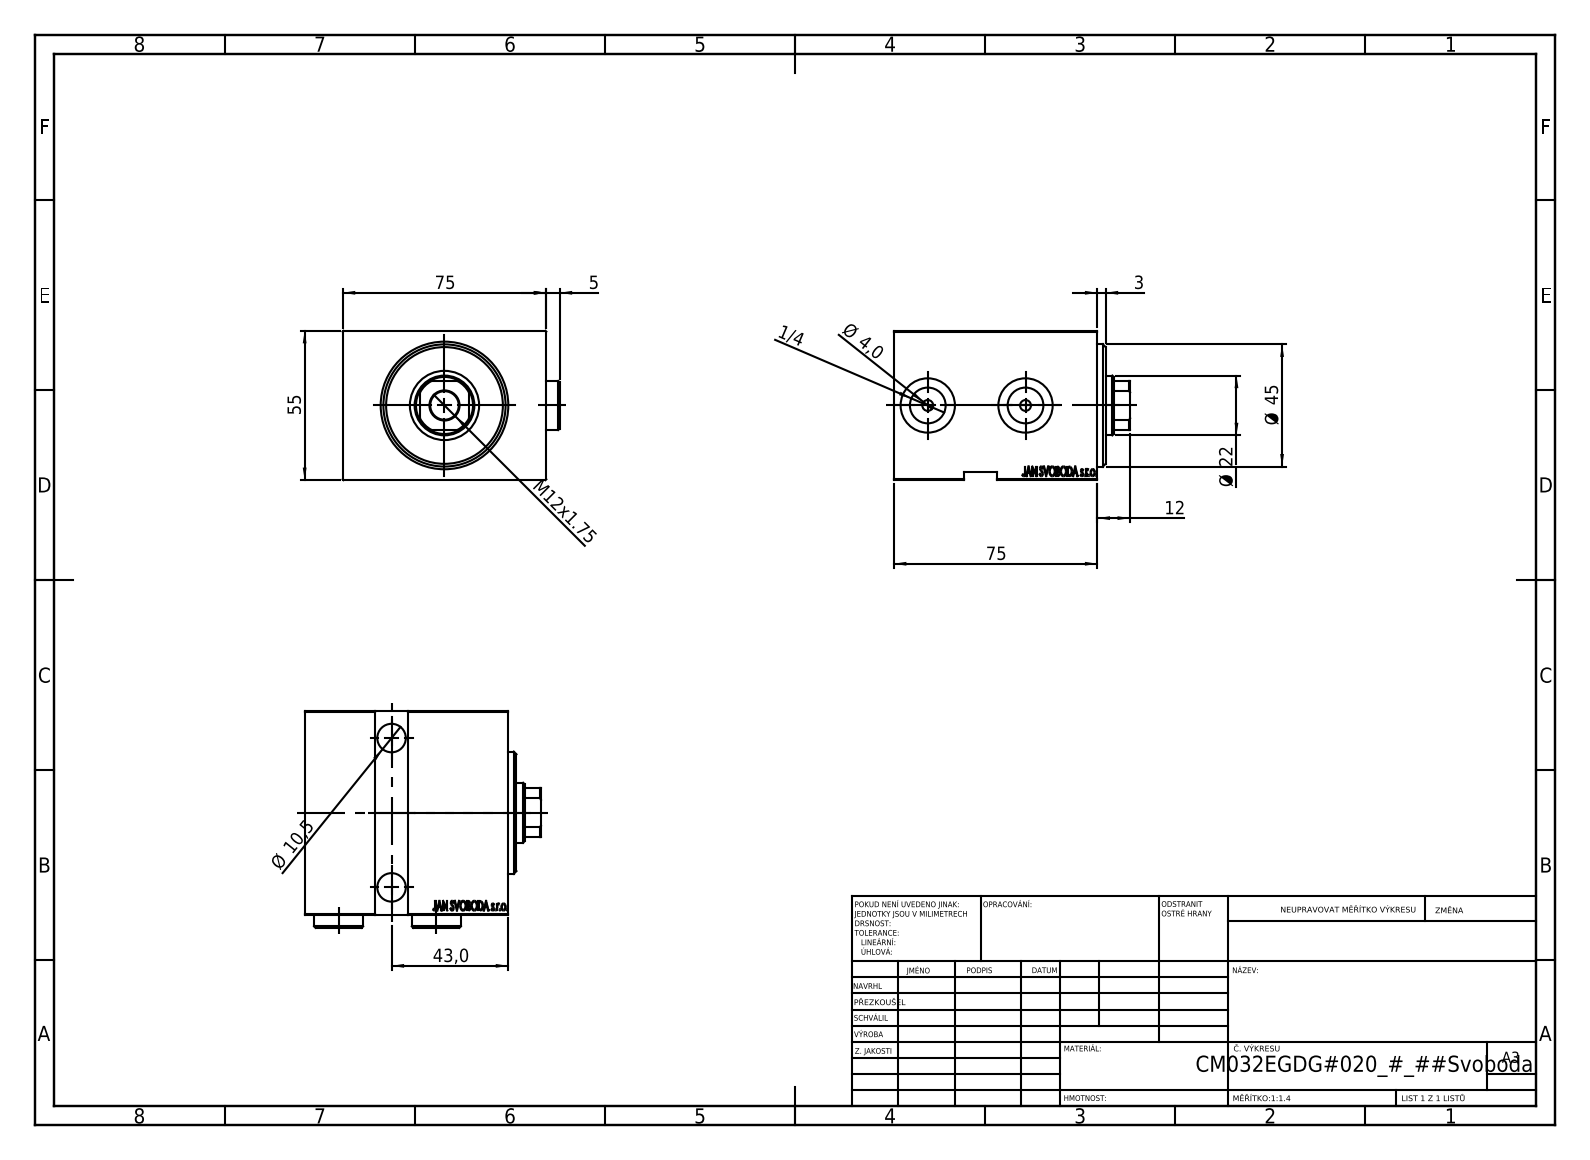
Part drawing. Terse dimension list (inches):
name: V450CM_E_VCP; V450CM_VC_B; Zatka_OIL_PORT; V450CM_E_Body
written by: SolidWorks 2019 (CONFIG_CONTROL_DESIGN)
unit: in
bodies: 5 solids, 899 faces (443 planar, 58 cylindrical, 398 other)
size: 3.425 × 3.146 × 2.165
volume: 17.38 in³; area: 86.78 in²
holes: 3× ⌀0.413, 2× ⌀0.157, 2× ⌀0.518, 2× ⌀0.65, 2× ⌀0.787, 1× ⌀0.866, 1× ⌀1.004, 1× ⌀1.26, 1× ⌀1.772
bosses: 2× ⌀0.709, 1× ⌀1.339
rounds: 1× R0.413
face distances: 2.953, 2.165, 0.197, 0.118, 2.559, 0.394, 2.756, 2.362, 2.949, 0.472
hole spacings: 1.417, 2.165
